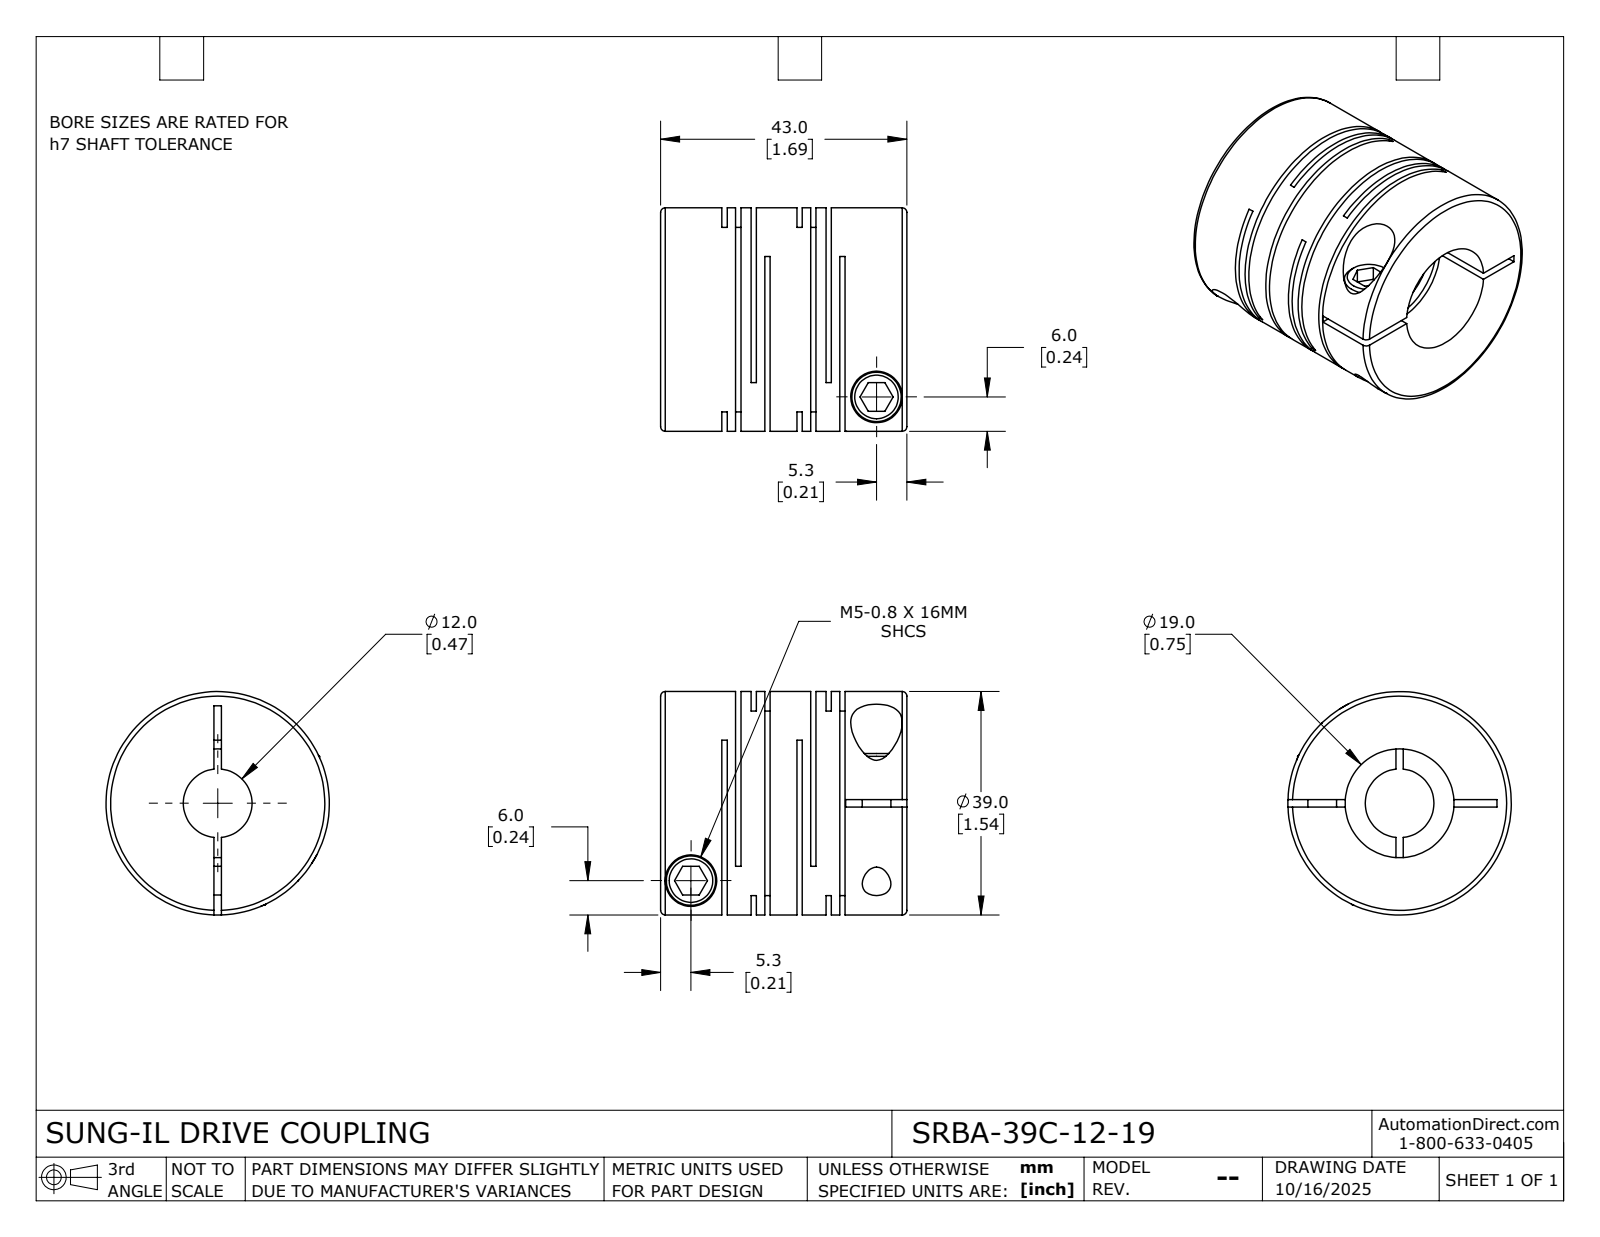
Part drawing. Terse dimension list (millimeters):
name: SRBA-39C-12-19
written by: SolidWorks 2024 (CONFIG_CONTROL_DESIGN)
unit: mm
bodies: 1 solid, 115 faces (60 planar, 42 cylindrical, 13 other)
size: 43 × 39 × 39
volume: 34 234 mm³; area: 21 915 mm²
holes: 2× ⌀5, 2× ⌀9, 1× ⌀12, 1× ⌀19
bosses: 2× ⌀8.6, 1× ⌀39
face distances: 13.1, 0.92, 2.4, 5.1, 10.7, 14.02, 18.2, 12.18, 3.32, 7.5
